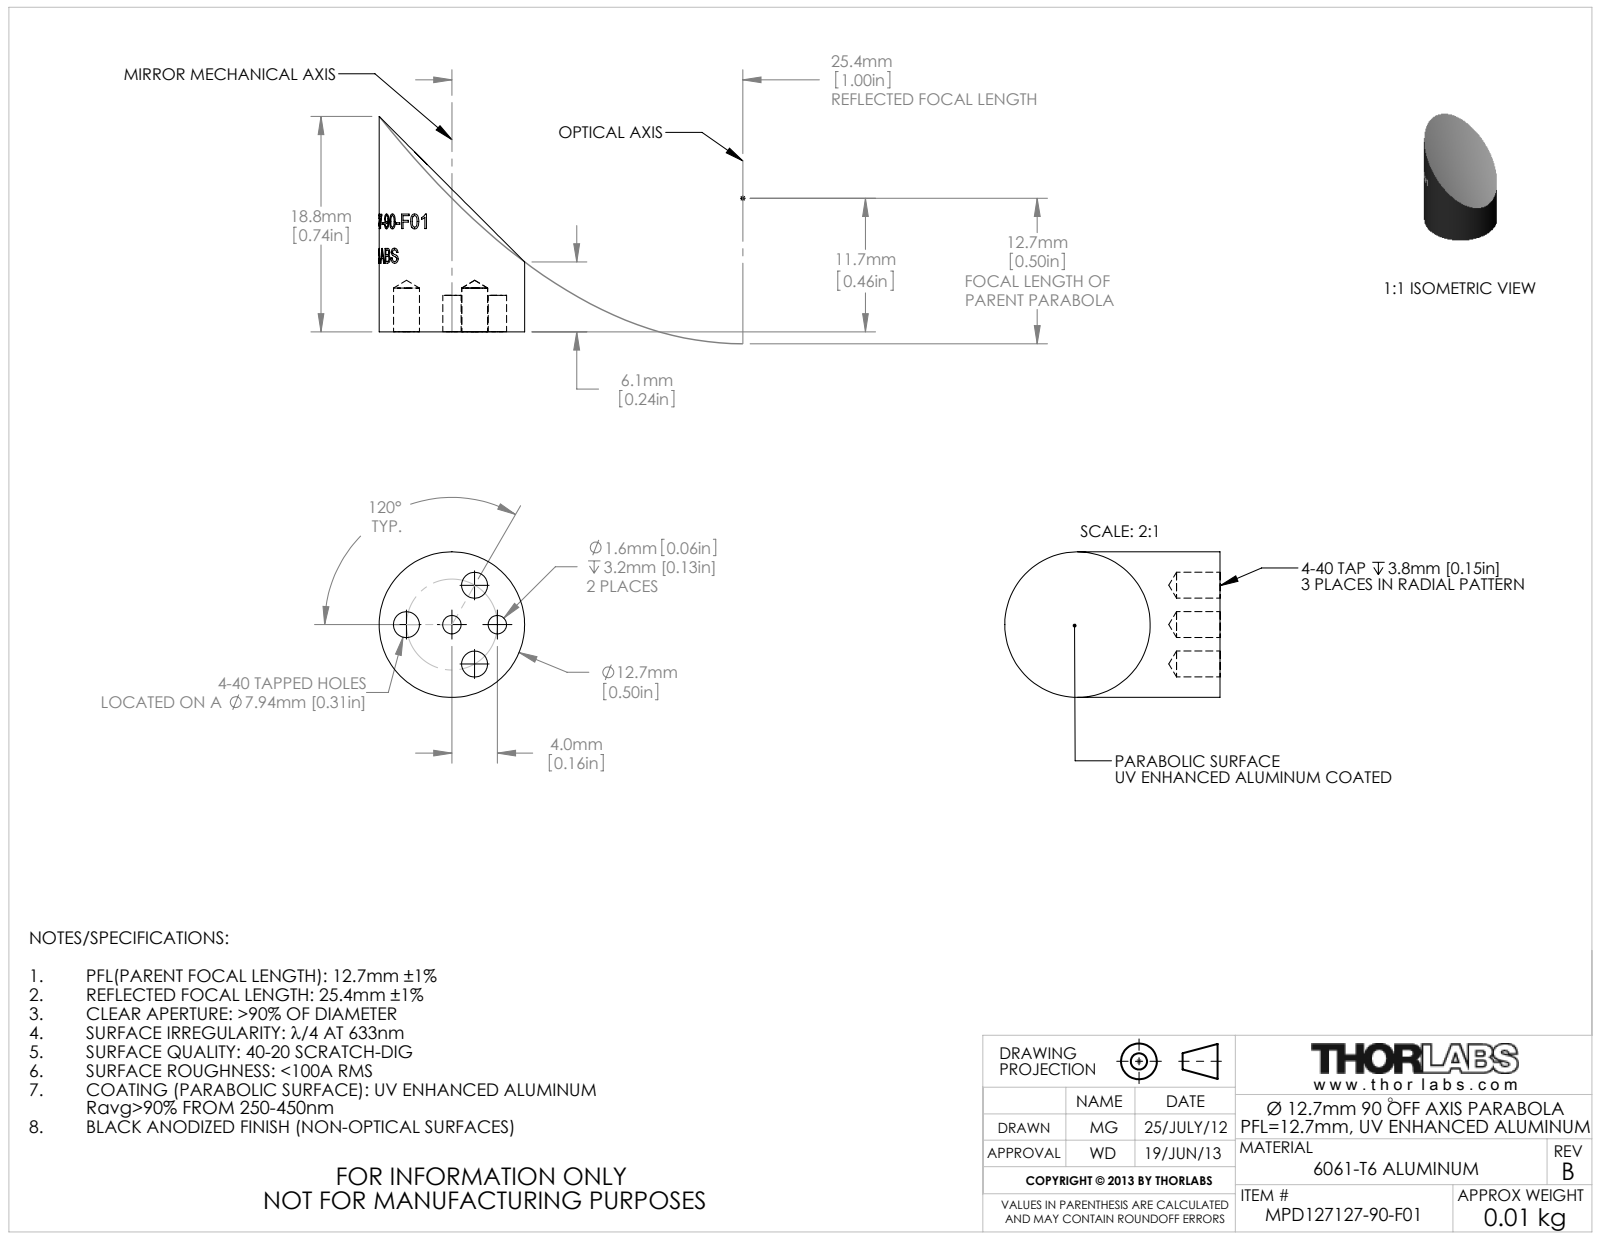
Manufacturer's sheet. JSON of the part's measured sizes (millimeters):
{"part_name": "24686-E0W", "step_written_by": "SolidWorks 2012 (CONFIG_CONTROL_DESIGN)", "units": "millimeters", "bodies": {"solids": 1, "faces": 57, "planar": 3, "cylindrical": 46, "other": 8}, "overall_size": [18.8, 12.7, 12.7], "volume_mm3": 1465, "surface_area_mm2": 919, "round_holes": [[2.26, 3], [1.6, 2]], "round_bosses_or_shafts": [[12.7, 1]], "face_to_face_distances": [3.17], "hole_center_spacings": [3.97, 6.87, 6.88, 7.94]}
